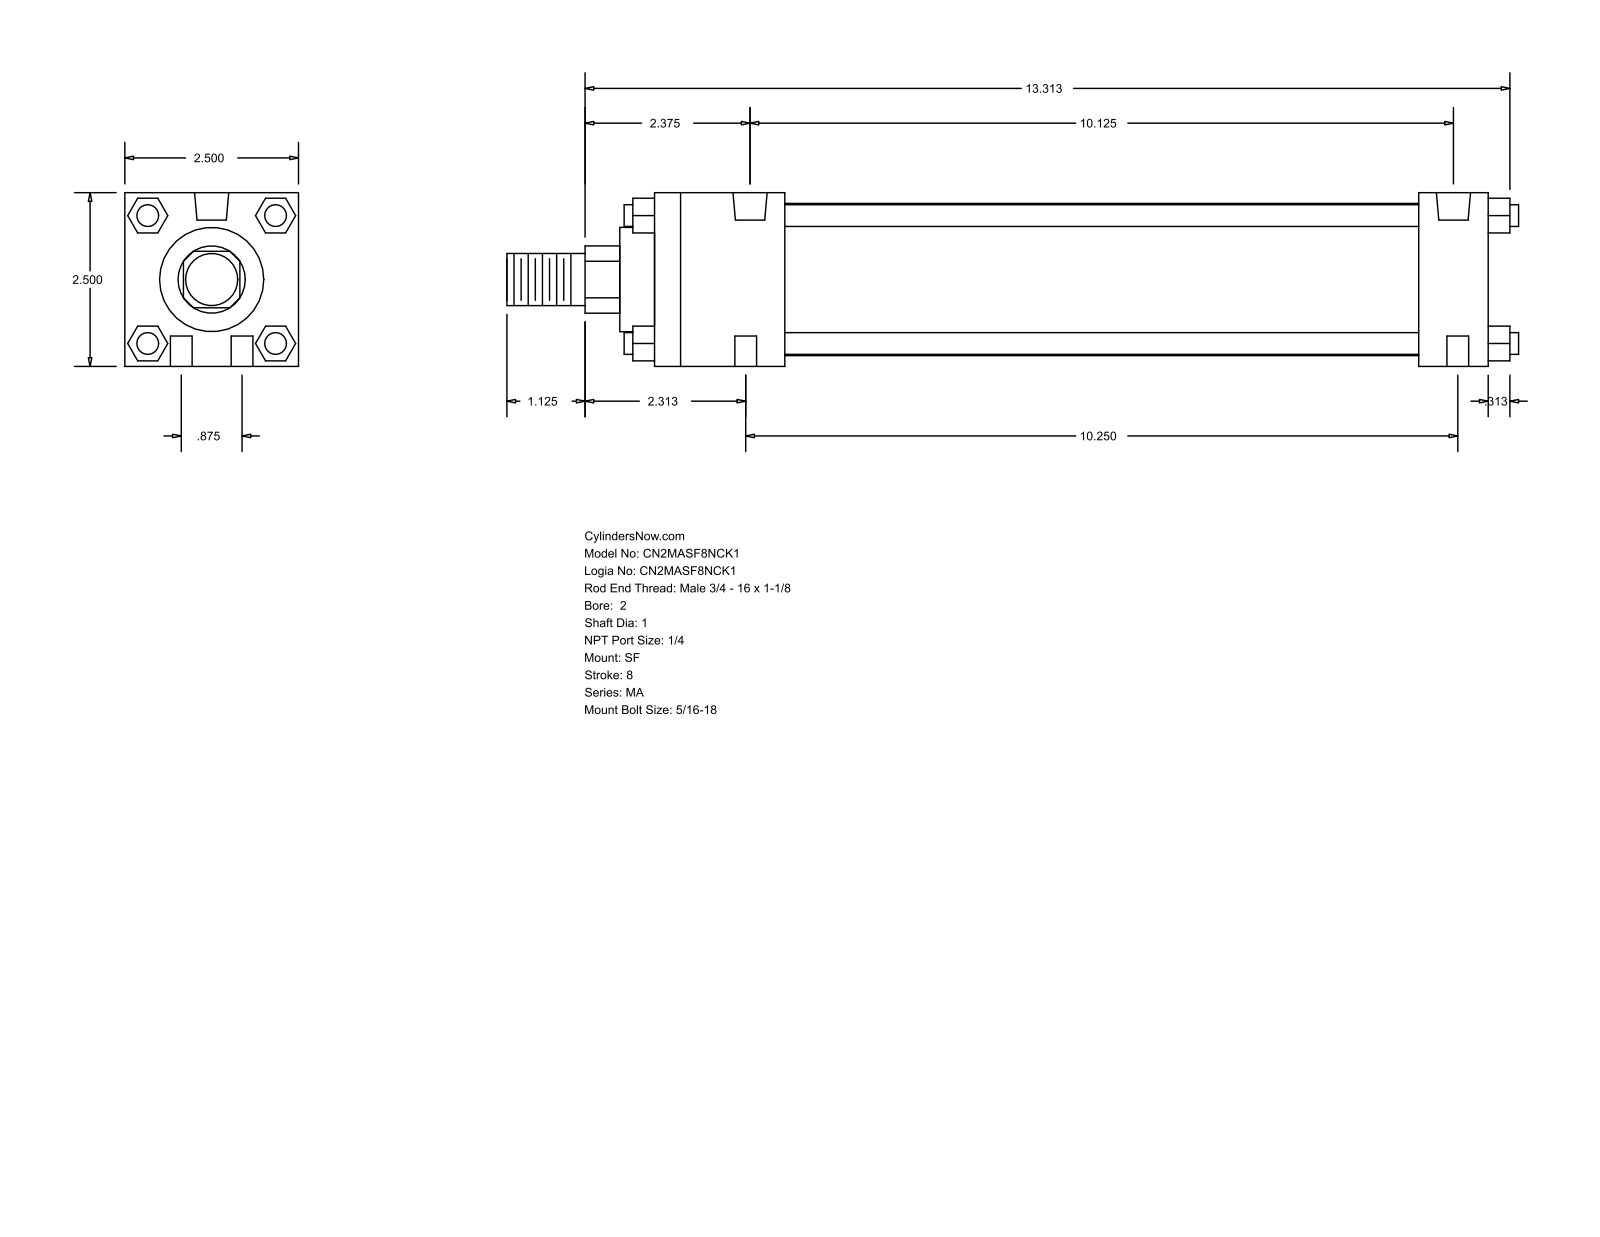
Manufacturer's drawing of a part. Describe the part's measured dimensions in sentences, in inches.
The part is named "MA_SF__0200_1". Its 3-D file was written by "GSSL Pune (CONFIG_CONTROL_DESIGN)". It is 0 solids with 124 faces: 94 planar, 30 cylindrical and 0 other. Overall it measures 14.563 by 2.5 by 2.5 inches. Round holes: 6 of diameter 0.313, 2 of diameter 0.492. Round bosses or shafts: 4 of diameter 0.313, 1 of diameter 2.19, 1 of diameter 1.5, 1 of diameter 1, 1 of diameter 0.75. Partial cylindrical surfaces (rounded edges, fillets, slot ends): 1 of radius 0.484. The main face-to-face distances are 2.5, 12, 0.5, 1, 11, 1.875, 9.125, 10.125, 0.92, 1.593. The hole center spacings are 0.442, 10.197, 0.875, 10.125, 10.25, 10.287.
